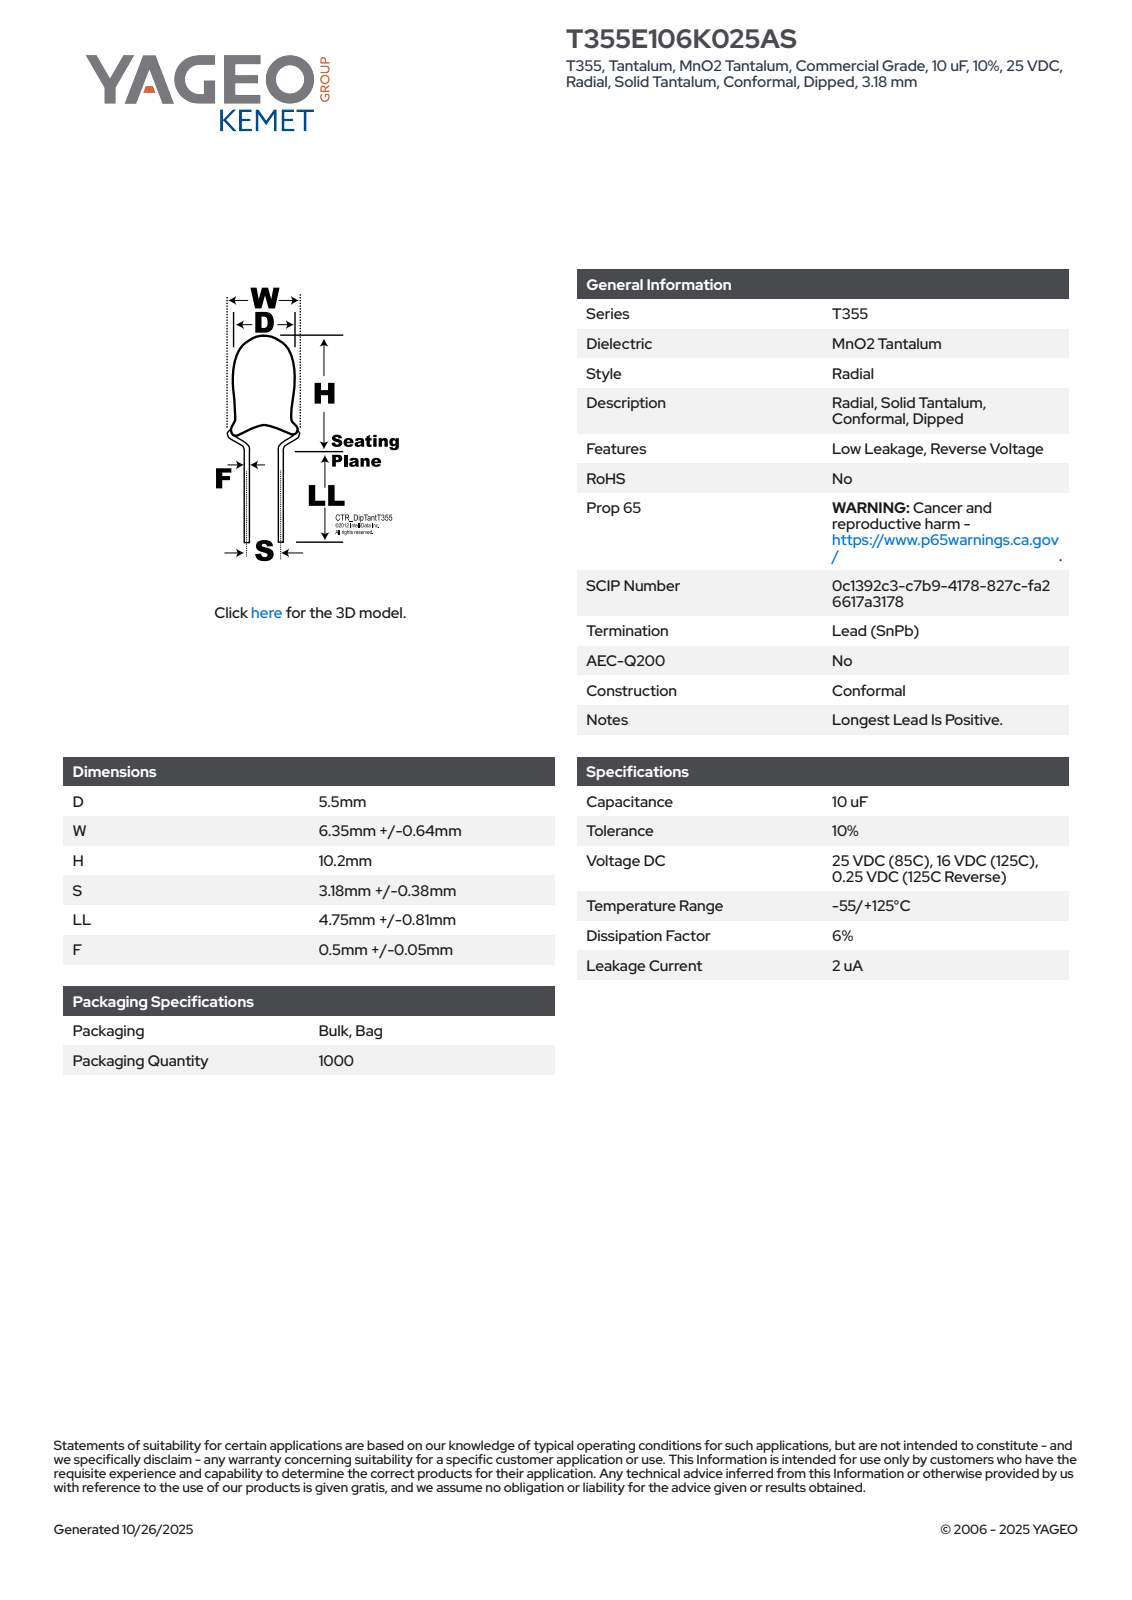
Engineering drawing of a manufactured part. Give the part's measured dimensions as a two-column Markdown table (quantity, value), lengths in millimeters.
| quantity | value |
| --- | --- |
| part name | CTR_T355_D5.5W6.99H10.2S3.18LL5.56F0.55 |
| STEP written by | SolidWorks 2021 (AUTOMOTIVE_DESIGN) |
| units | millimeters |
| bodies | 1 solid, 100 faces (30 planar, 6 cylindrical, 64 other) |
| overall size | 15.76 × 6.99 × 5.5 |
| volume | 145 mm³ |
| surface area | 176 mm² |
| round bosses / shafts (diameter × count) | 5.5 × 1 |
| partial cylindrical surfaces (radius × count) | 2.74 × 1 |
| main face-to-face distances | 7.12, 8.64, 15.76, 12.59, 3.95, 3.17, 11.99, 3.35, 0.6, 3.77 |
